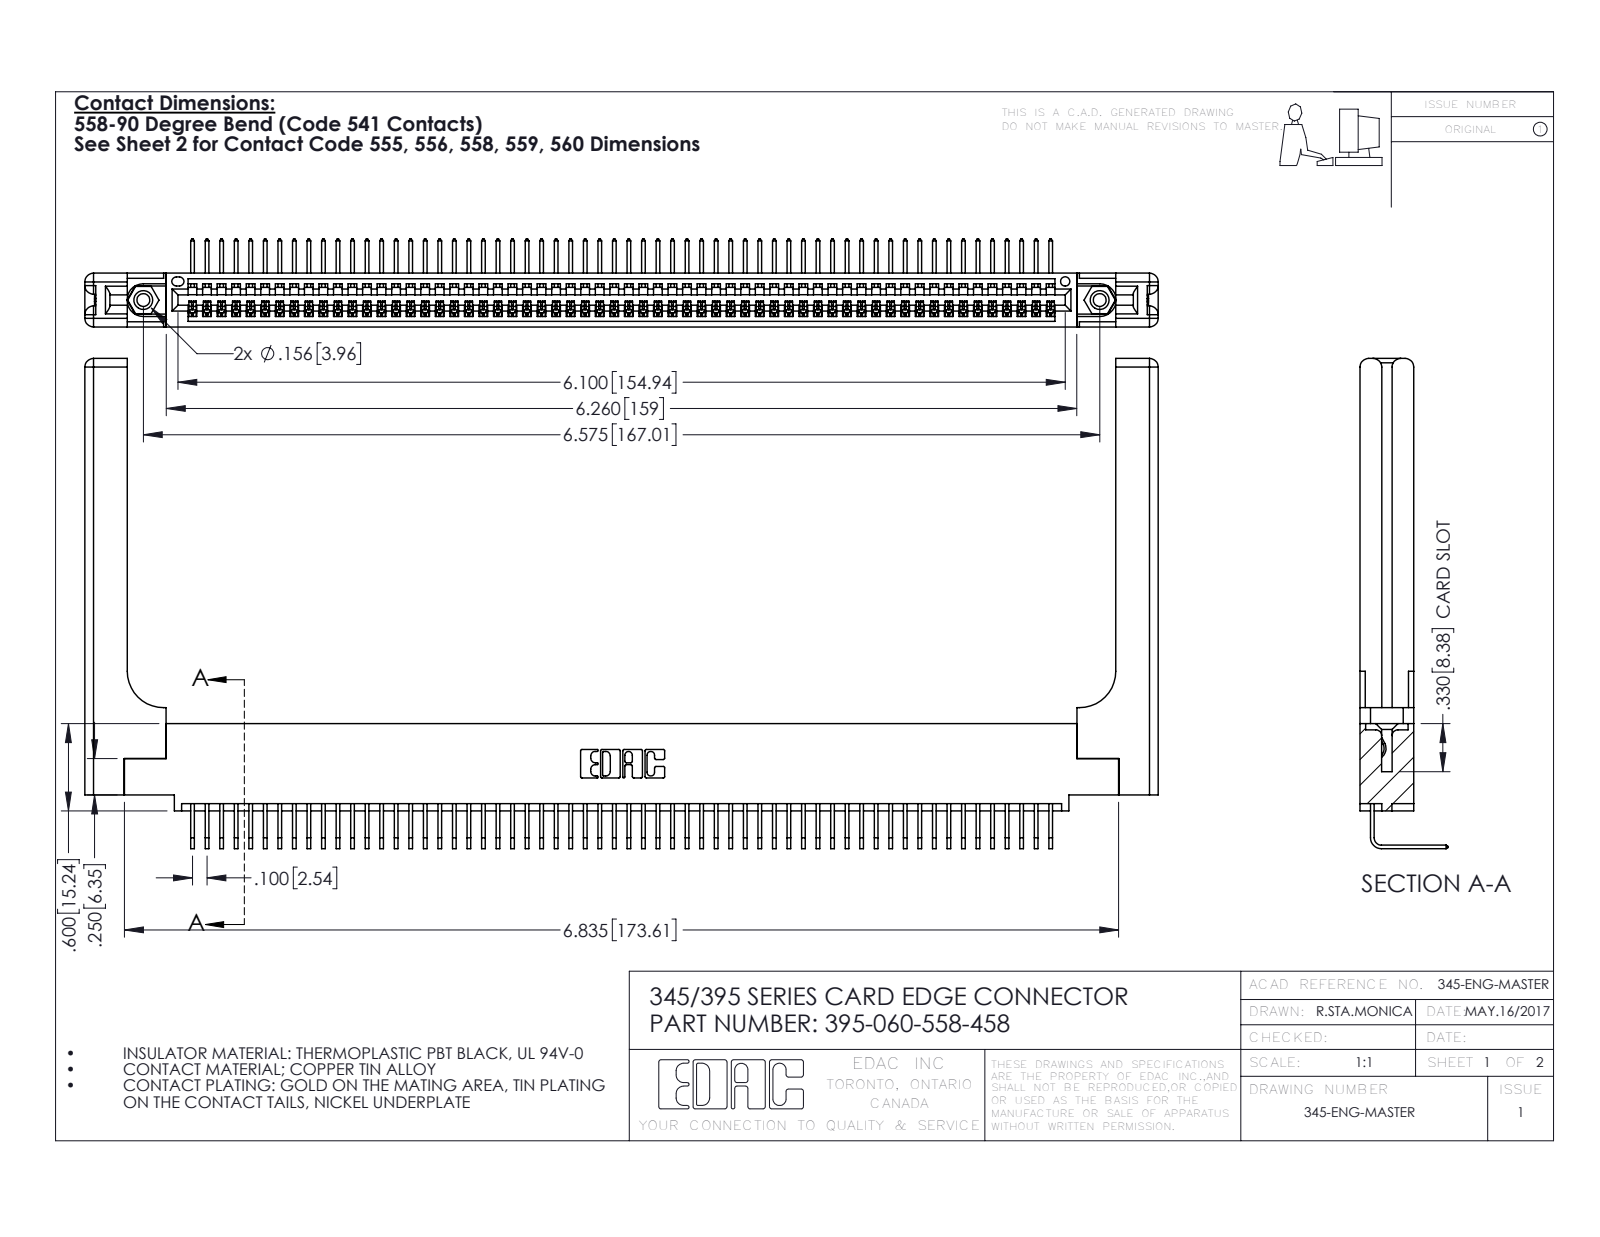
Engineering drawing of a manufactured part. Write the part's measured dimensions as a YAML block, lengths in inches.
part_name: "395-060-558-458; 345-292-001_558 Tail - 2; 345-250-001_345-250-001-102; 345 Part_0.110 Offset - 0.156 Dia-TH (+1 more)"
step_written_by: "SolidWorks 2016 (CONFIG_CONTROL_DESIGN)"
units: inches
bodies: {solids: 65, faces: 3986, planar: 2752, cylindrical: 1174, other: 60}
overall_size: [7.379, 3.369, 0.605]
volume: 1.622
surface_area: 47.78
round_holes:
  - {diameter: 0.089, count: 2}
  - {diameter: 0.125, count: 2}
  - {diameter: 0.156, count: 2}
  - {diameter: 0.064, count: 1}
round_bosses_or_shafts:
  - {diameter: 0.155, count: 2}
partial_cylinders:
  - {radius: 0.006, count: 120}
  - {radius: 0.01, count: 22}
  - {radius: 0.06, count: 16}
  - {radius: 0.007, count: 6}
  - {radius: 0.031, count: 6}
  - {radius: 0.026, count: 3}
  - {radius: 0.03, count: 2}
  - {radius: 0.031, count: 2}
face_to_face_distances: [0.072, 0.37, 0.298, 0.098, 0.272, 0.025, 0.2, 0.225, 0.148, 0.15]
hole_center_spacings: [0.27, 6.339, 6.575]
